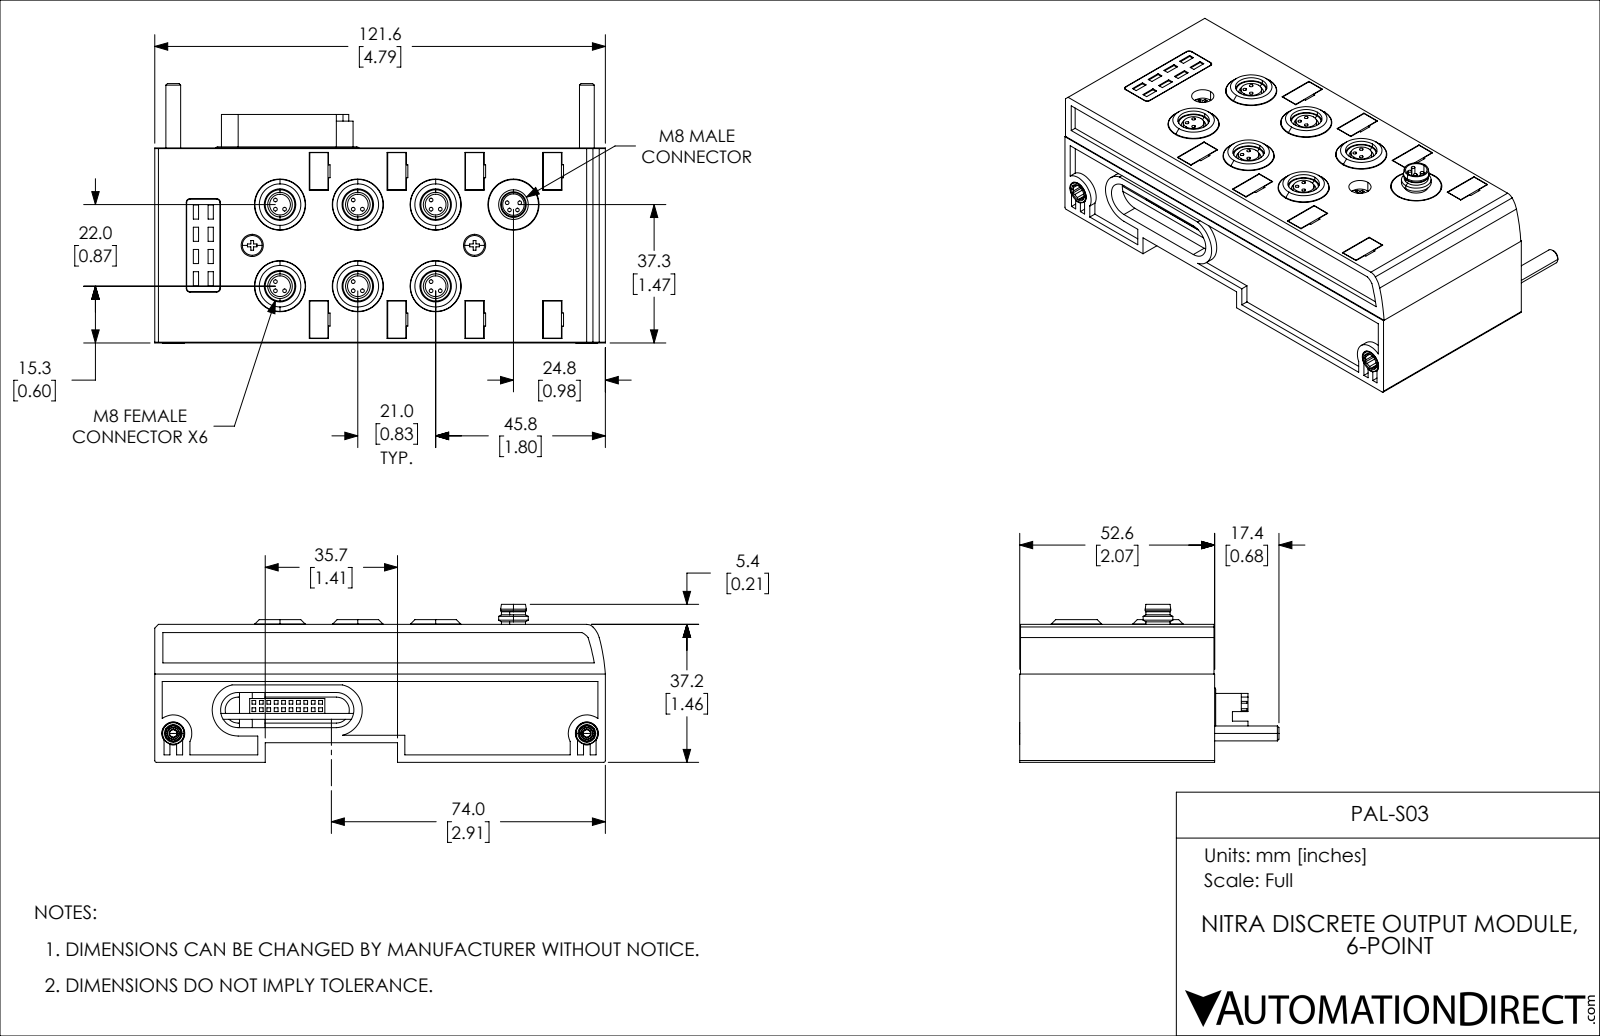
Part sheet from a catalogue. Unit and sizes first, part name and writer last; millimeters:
Units: millimetres
Overall size (bounding box): 121.6 × 70 × 42.6
Round holes (diameter × count): ⌀1 ×18, ⌀13.8 ×7, ⌀6.7 ×6, ⌀8.5 ×6, ⌀3.3 ×2, ⌀6 ×2, ⌀6.2 ×2, ⌀5.8 ×1
Round bosses / shafts (diameter × count): ⌀13.6 ×6, ⌀5.6 ×6, ⌀1 ×4, ⌀6.9 ×3, ⌀6 ×2, ⌀5.4 ×2, ⌀4 ×2, ⌀13.5 ×1
Partial cylindrical surfaces — rounded edges, fillets, slot ends (radius × count): R1 ×8, R0.5 ×2, R0.9 ×2, R2 ×2, R2.1 ×2, R3.5 ×2, R4.5 ×2, R4.7 ×2
Main face-to-face distances: 8, 13.4, 1.6, 13.2, 23.8, 37.2, 15.8, 29.2, 10.6, 5.2
Hole centre spacings: 1.8, 21, 30.4, 22.3, 19.8, 2.5, 22, 20.8
Volume: 145 600 mm³ · Surface area: 64 050 mm²
Bodies: 5 solids, 992 faces (668 planar, 214 cylindrical, 110 other)
Part name (STEP PRODUCT): PAL-S03
STEP written by: SolidWorks 2019 (CONFIG_CONTROL_DESIGN)
